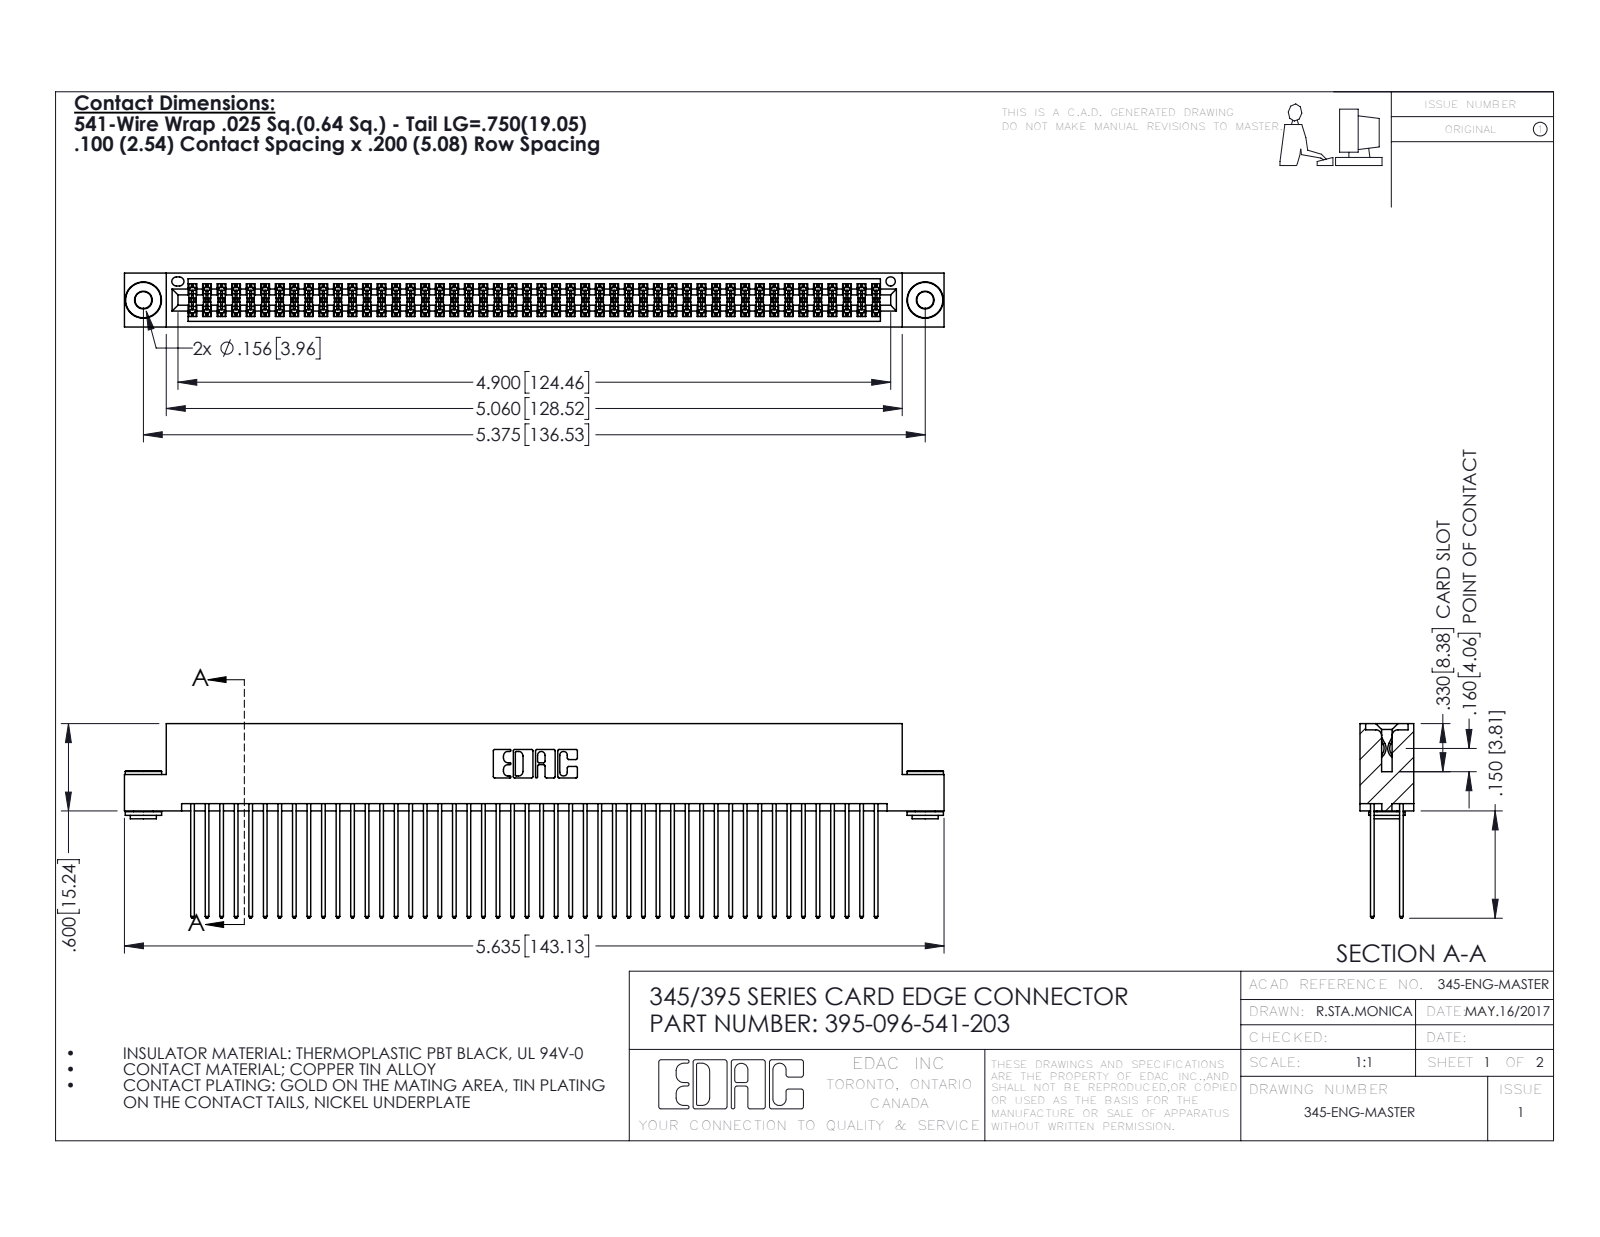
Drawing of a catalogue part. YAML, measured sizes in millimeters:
part_name: "345-292-001_345-293-141; 345 Part_Flush Mounting Lugs - 0.156 Dia-TH; 345-250-002_345-250-002-102; 395-096-541-203"
step_written_by: "SolidWorks 2016 (CONFIG_CONTROL_DESIGN)"
units: millimeters
bodies: {solids: 99, faces: 4964, planar: 3258, cylindrical: 1698, other: 8}
overall_size: [143.1, 34, 9.4]
volume: 14500
surface_area: 24390
round_holes:
  - {diameter: 2.9, count: 2}
  - {diameter: 4, count: 2}
  - {diameter: 1.6, count: 1}
round_bosses_or_shafts:
  - {diameter: 6.4, count: 2}
  - {diameter: 4.6, count: 2}
  - {diameter: 3.5, count: 2}
partial_cylinders:
  - {radius: 0.2, count: 144}
  - {radius: 0.3, count: 96}
  - {radius: 0.3, count: 22}
  - {radius: 0.2, count: 6}
  - {radius: 0.8, count: 6}
  - {radius: 0.7, count: 3}
  - {radius: 0.4, count: 2}
  - {radius: 0.5, count: 2}
face_to_face_distances: [1.8, 7.6, 5.1, 0.6, 2.5, 6.9, 5.7, 9.4, 4.4, 3.8]
hole_center_spacings: [6.9, 130.5, 136.5]
